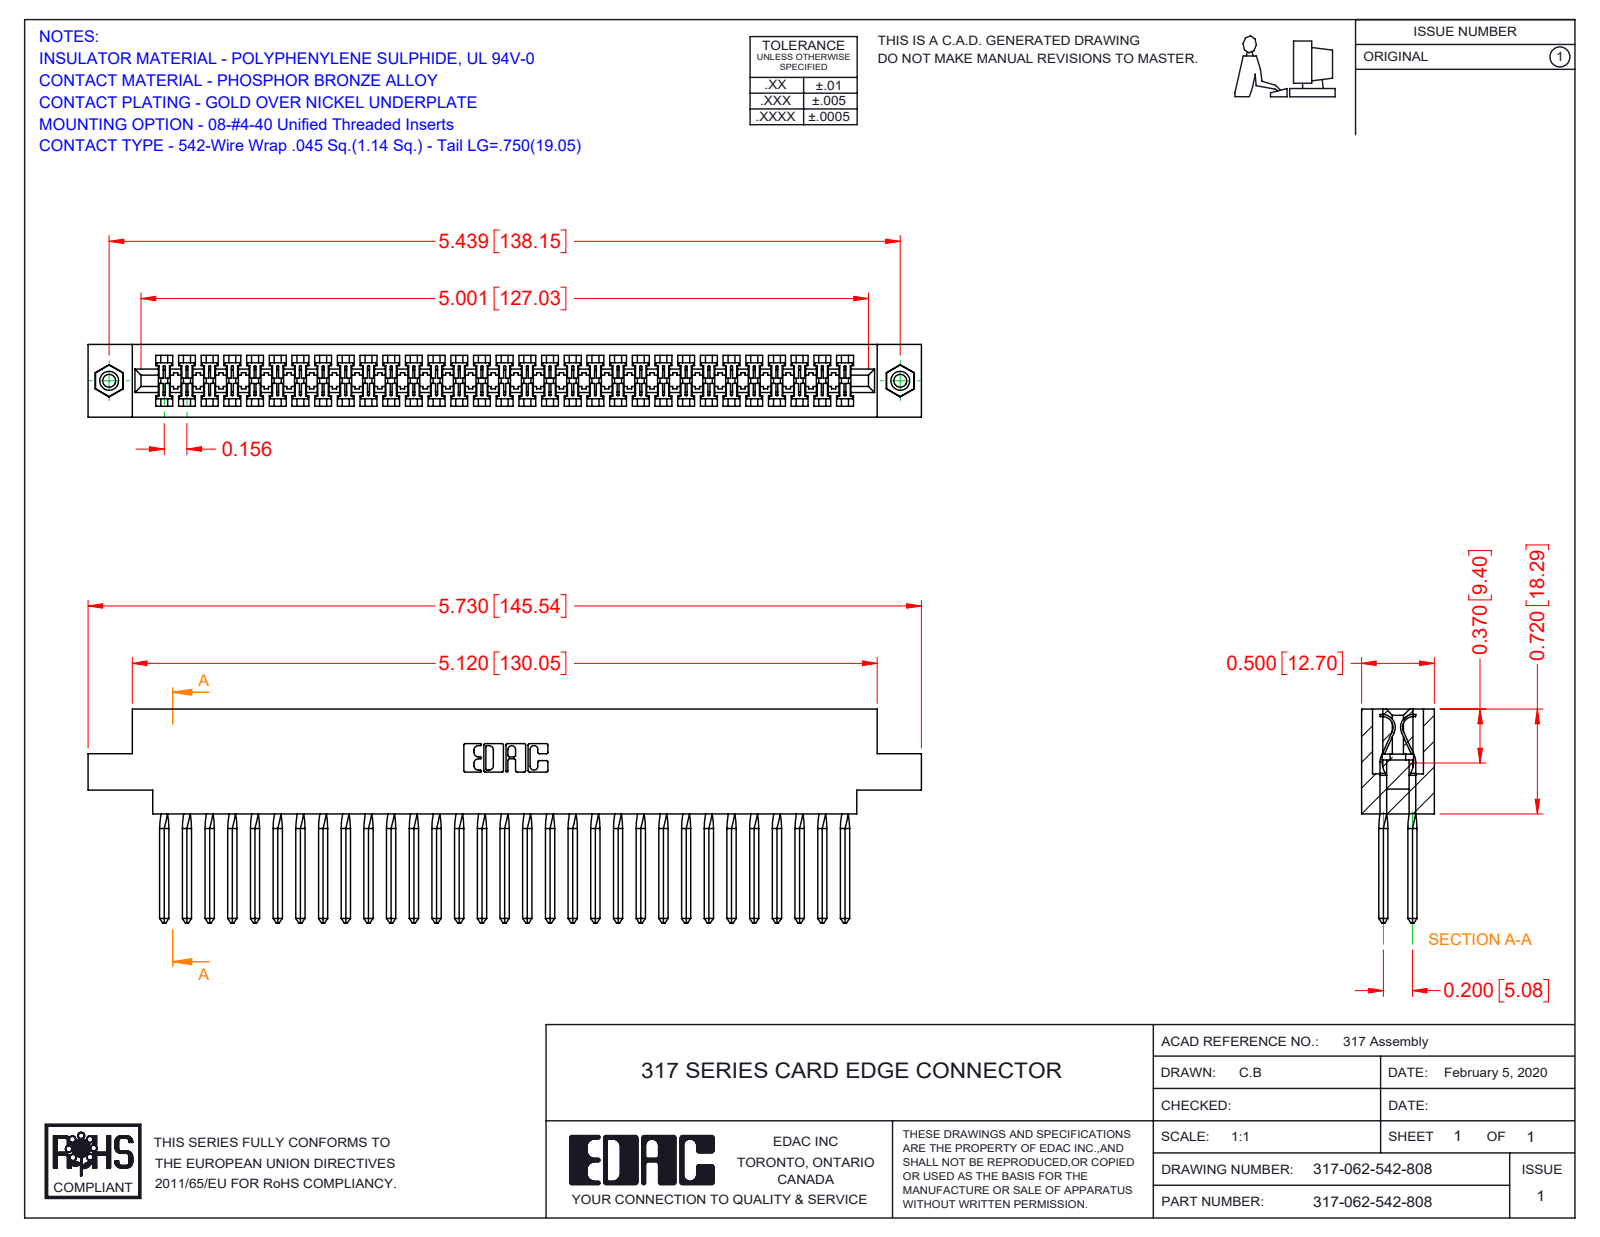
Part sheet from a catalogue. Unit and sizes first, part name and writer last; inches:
Units: inches
Overall size (bounding box): 5.73 × 1.47 × 0.5
Round holes (diameter × count): ⌀0.089 ×2, ⌀0.125 ×2, ⌀0.156 ×2
Round bosses / shafts (diameter × count): ⌀0.155 ×2
Partial cylindrical surfaces — rounded edges, fillets, slot ends (radius × count): R0.006 ×124, R0.01 ×22, R0.007 ×6, R0.031 ×6, R0.026 ×3, R0.074 ×2, R0.089 ×2, R0.1 ×2
Main face-to-face distances: 0.5, 0.075, 0.425, 0.35, 0.2, 0.11, 0.116, 0.046, 0.136, 0.128
Hole centre spacings: 5.439
Volume: 1.433 in³ · Surface area: 50.09 in²
Bodies: 65 solids, 3696 faces (2942 planar, 490 cylindrical, 264 other)
Part name (STEP PRODUCT): 317-290-003_542; 317 Part_.156 Dia - TI; 317-062-542-878; 345-250-001_345-250-003-102
STEP written by: SolidWorks 2016 (CONFIG_CONTROL_DESIGN)
